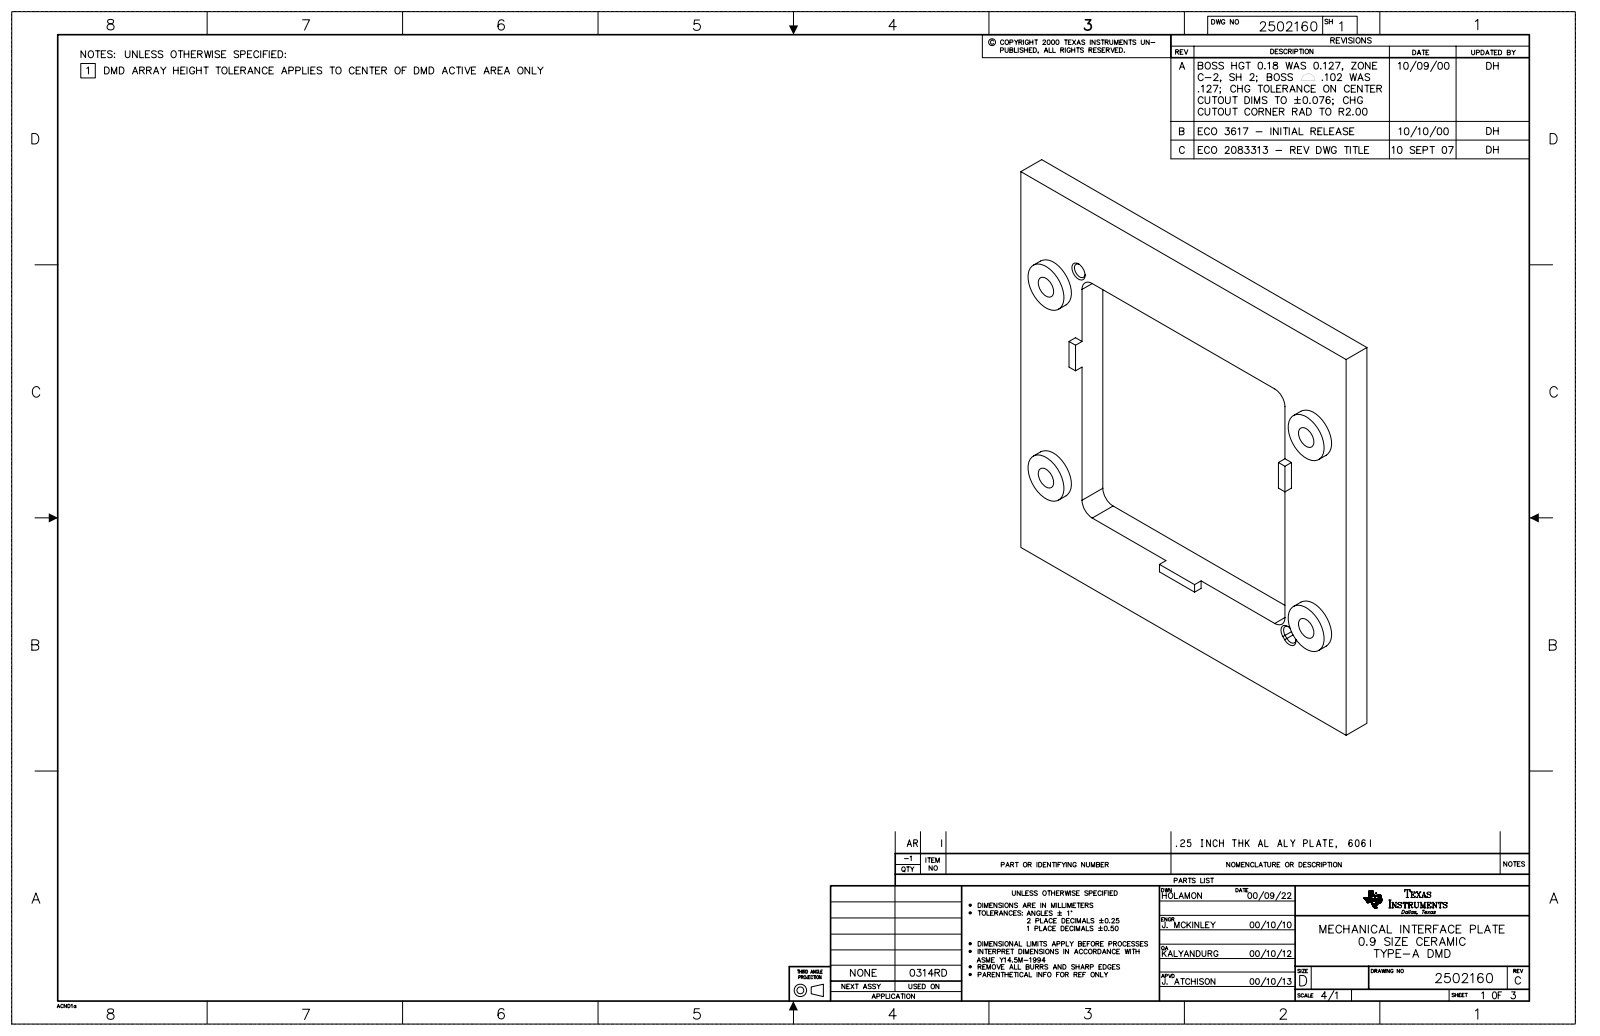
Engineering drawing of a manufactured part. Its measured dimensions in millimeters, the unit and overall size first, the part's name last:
Units: millimetres
Overall size (bounding box): 63.5 × 63.5 × 5.51
Round holes (diameter × count): ⌀3 ×4, ⌀2.08 ×1
Round bosses / shafts (diameter × count): ⌀7 ×4
Partial cylindrical surfaces — rounded edges, fillets, slot ends (radius × count): R2 ×4, R1.04 ×2
Main face-to-face distances: 4.06, 63.5, 11.94, 51.56, 51.57, 39.63, 11.93, 39.62, 5.51, 1.45
Hole centre spacings: 32.26, 50.8, 60.18, 6.57, 36.96, 46.11, 58.72
Volume: 10 080 mm³ · Surface area: 6 961 mm²
Bodies: 1 solid, 62 faces (30 planar, 26 cylindrical, 6 other)
Part name (STEP PRODUCT): 2502160B; SXIF
STEP written by: AutoCAD 2000i (CONFIG_CONTROL_DESIGN)
